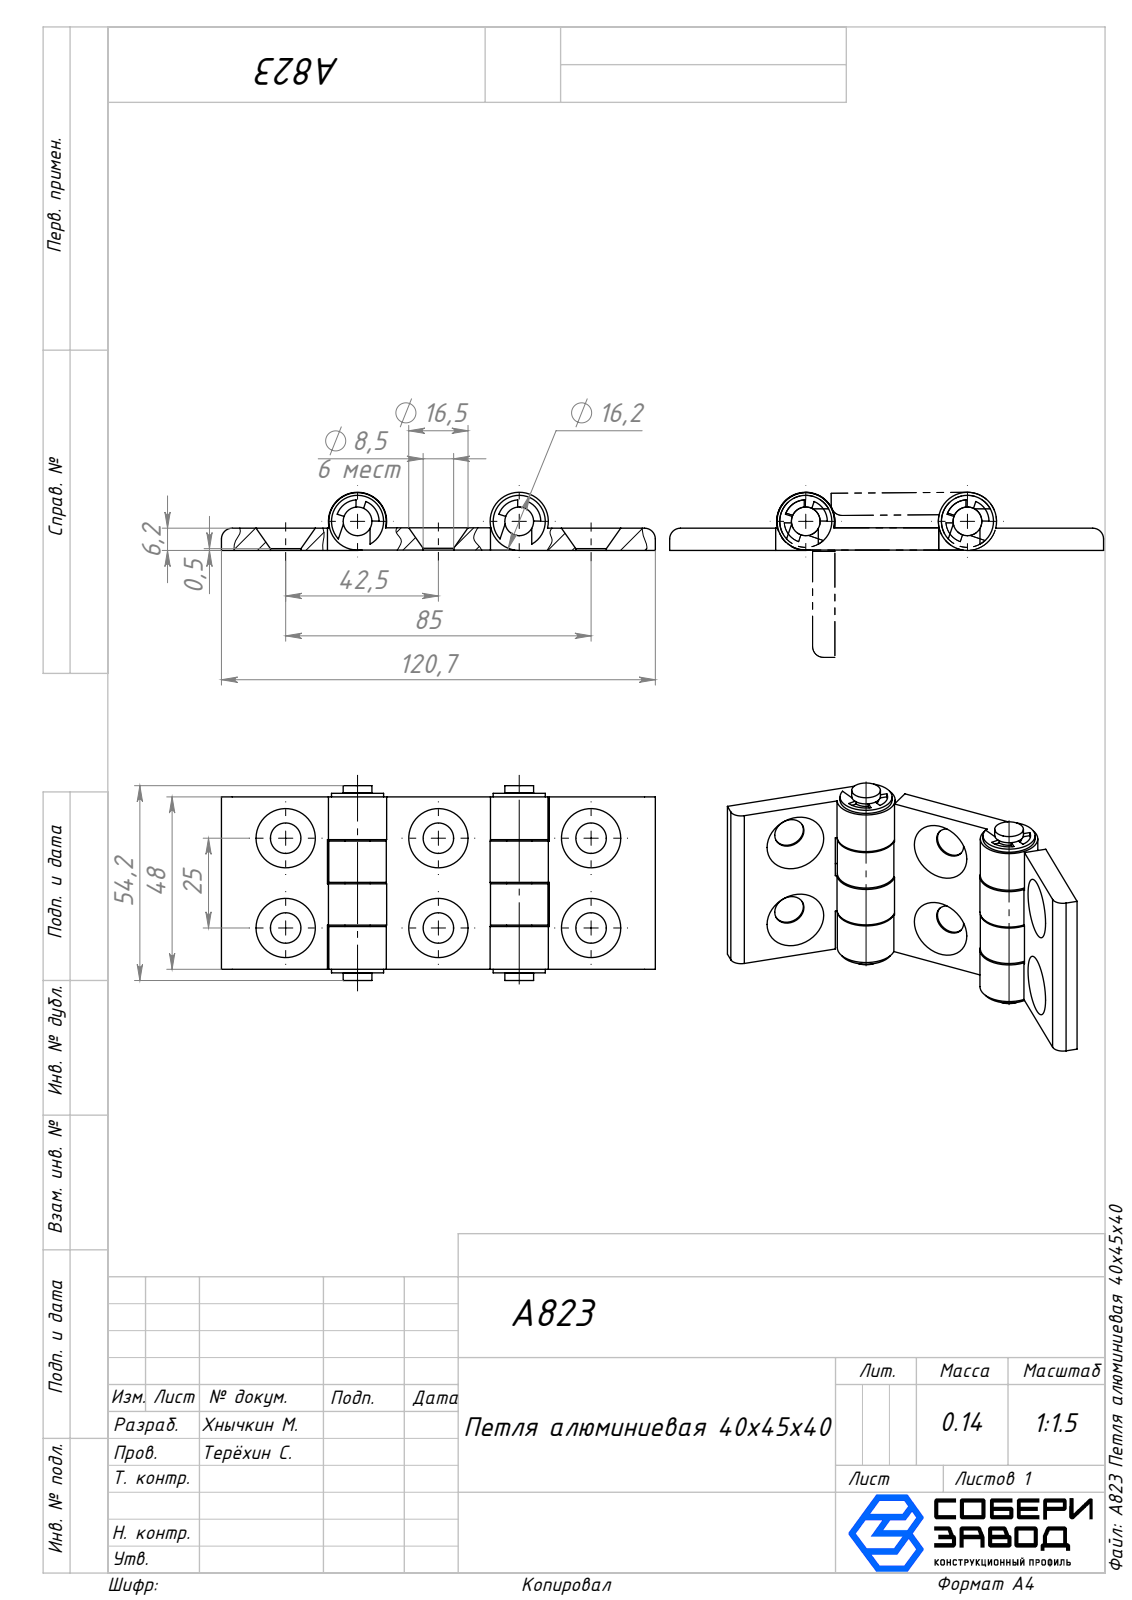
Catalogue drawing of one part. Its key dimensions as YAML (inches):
part_name: "A823 Сред петля_00; A823 Петля алюминиевая 40x45x40; A823 Палец_01; A823 Петля, часть 40 серии_00 (+1 more)"
step_written_by: "SolidWorks 2025 (AUTOMOTIVE_DESIGN)"
units: inches
bodies: {solids: 9, faces: 180, planar: 74, cylindrical: 94, other: 12}
overall_size: [4.754, 2.136, 0.638]
volume: 2.614
surface_area: 36.64
round_holes:
  - {diameter: 0.335, count: 6}
  - {diameter: 0.276, count: 2}
round_bosses_or_shafts:
  - {diameter: 0.315, count: 2}
partial_cylinders:
  - {radius: 0.118, count: 2}
  - {radius: 0.236, count: 2}
  - {radius: 0.285, count: 2}
  - {radius: 0.315, count: 2}
  - {radius: 0.319, count: 2}
face_to_face_distances: [0.244, 0.469, 0.24, 0.484, 0.937, 0.953, 0.016, 1.89, 0.248, 1.421]
hole_center_spacings: [1.673, 1.941, 0.984, 3.346, 3.487, 1.771]
